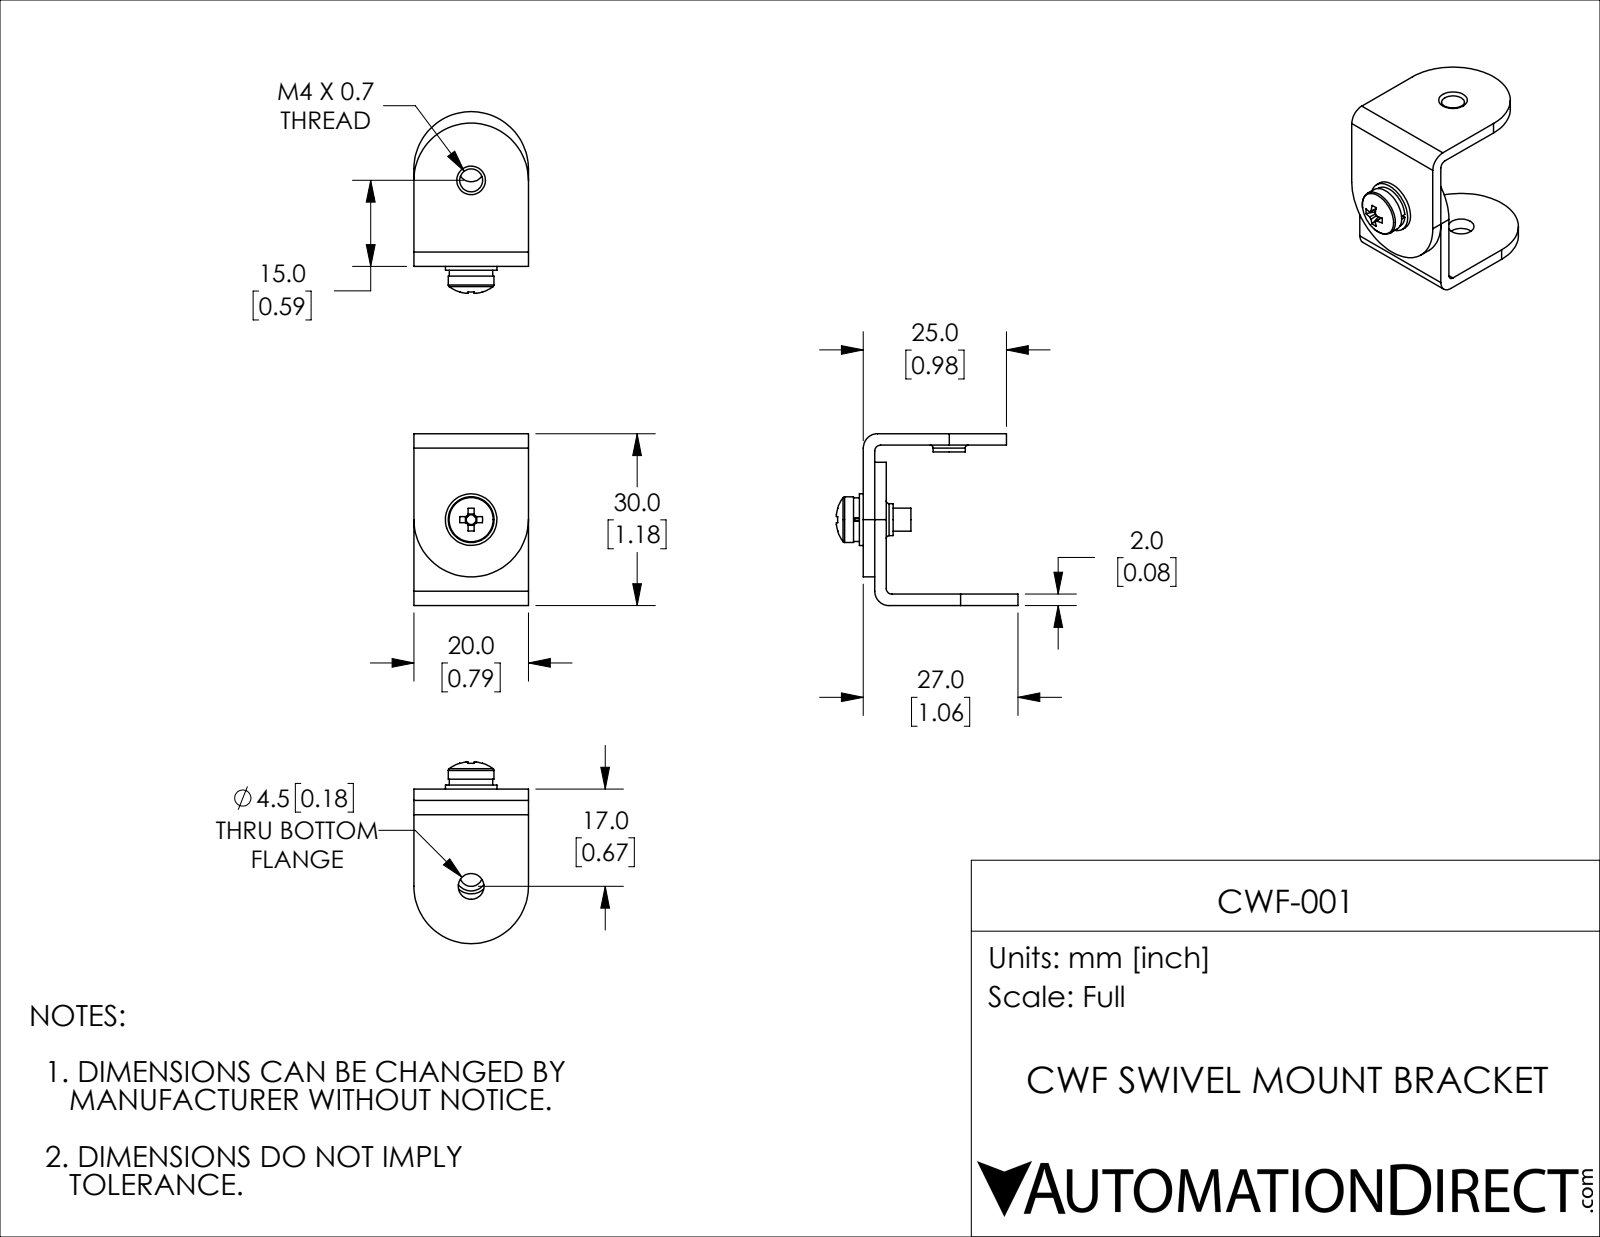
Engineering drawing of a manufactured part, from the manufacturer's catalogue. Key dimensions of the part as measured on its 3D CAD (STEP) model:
Part name (STEP PRODUCT): CWF-001
STEP written by: SolidWorks 2018 (AUTOMOTIVE_DESIGN)
Units: inches
Bodies: 5 solids, 89 faces (38 planar, 32 cylindrical, 19 other)
Overall size (bounding box): 1.249 × 1.181 × 0.787
Volume: 0.224 in³ · Surface area: 6.951 in²
Round holes (diameter × count): ⌀0.157 ×2, ⌀0.177 ×2, ⌀0.161 ×1, ⌀0.169 ×1
Round bosses / shafts (diameter × count): ⌀0.22 ×2, ⌀0.787 ×1, ⌀0.354 ×1, ⌀0.315 ×1, ⌀0.299 ×1
Partial cylindrical surfaces — rounded edges, fillets, slot ends (radius × count): R0.039 ×2, R0.098 ×2, R0.394 ×2
Main face-to-face distances: 0.079, 1.102, 1.181, 0.157, 1.024, 0.787, 0.185, 0.106, 0.028, 0.224
Hole centre spacings: 0.079
